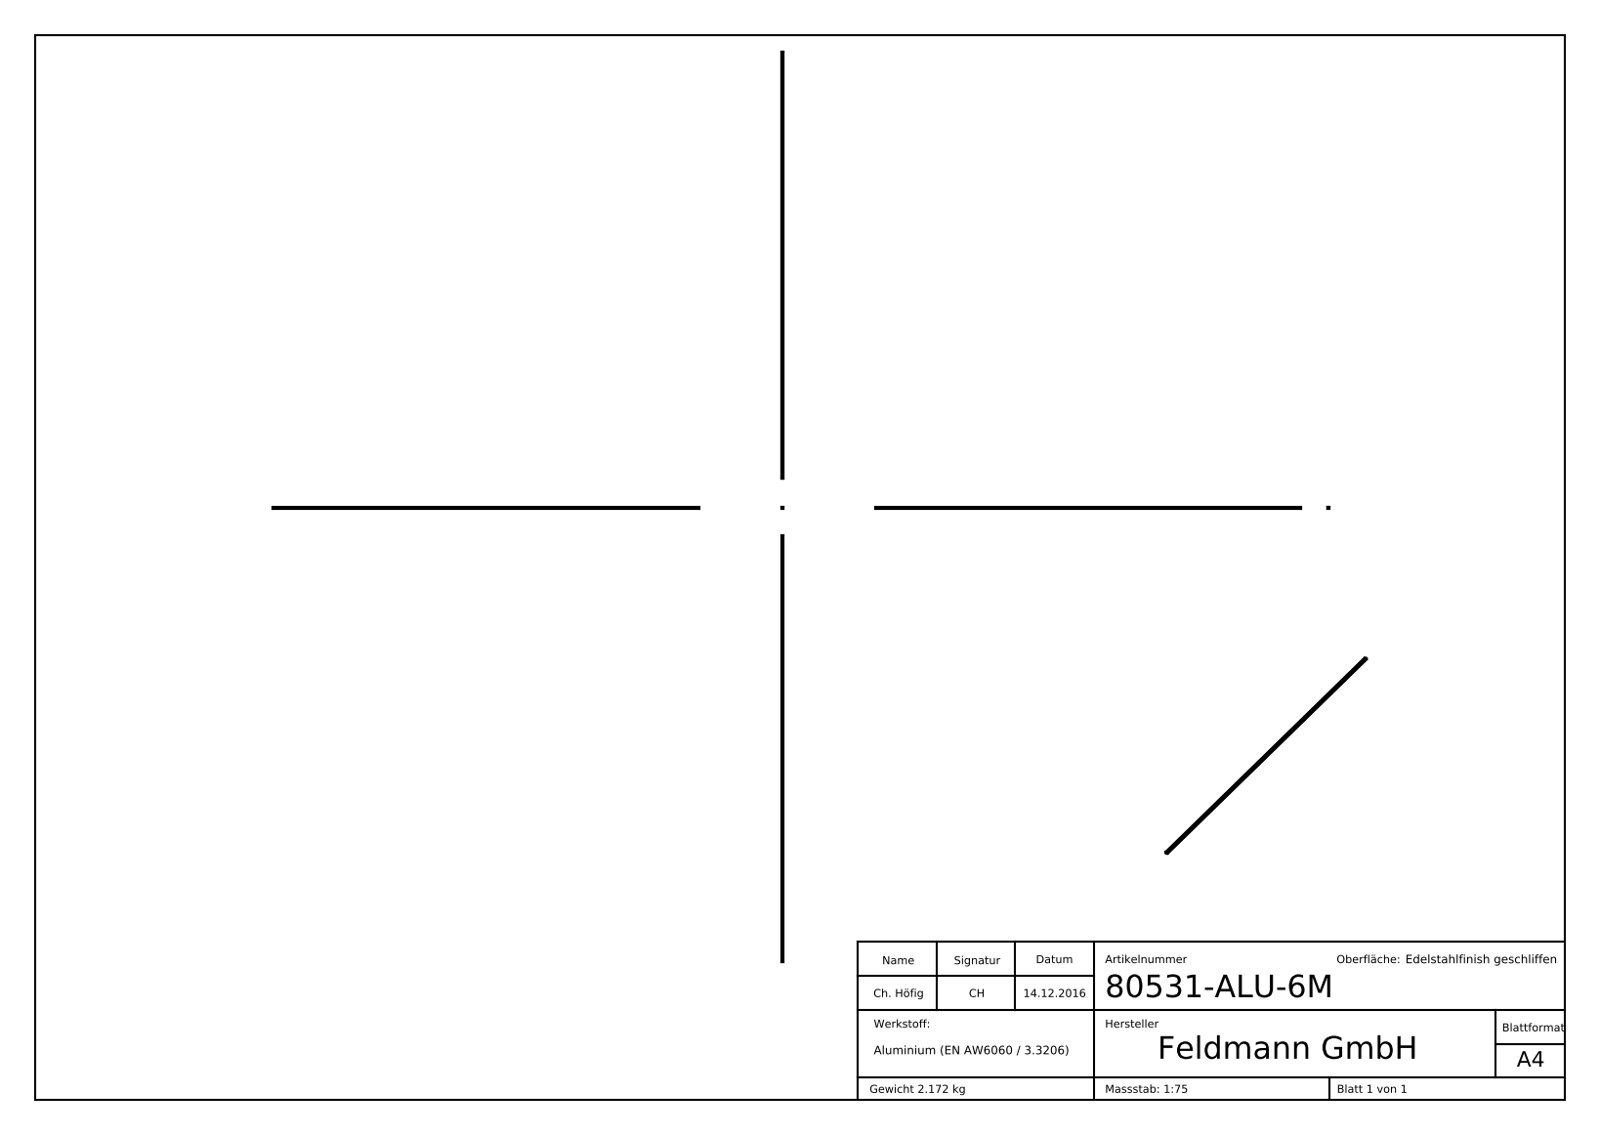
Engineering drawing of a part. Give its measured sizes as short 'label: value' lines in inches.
name: 80531-ALU-6M
written by: SolidWorks 2015 (CONFIG_CONTROL_DESIGN)
unit: in
bodies: 1 solid, 283 faces (151 planar, 6 cylindrical, 126 other)
size: 236.22 × 1.26 × 0.787
volume: 49.09 in³; area: 1 278 in²
rounds: 4× R0.02, 2× R0.079
face distances: 0.079, 1.181, 1.26, 1.102, 0.709, 0.787, 236.22, 0.075, 1.106, 1.185
